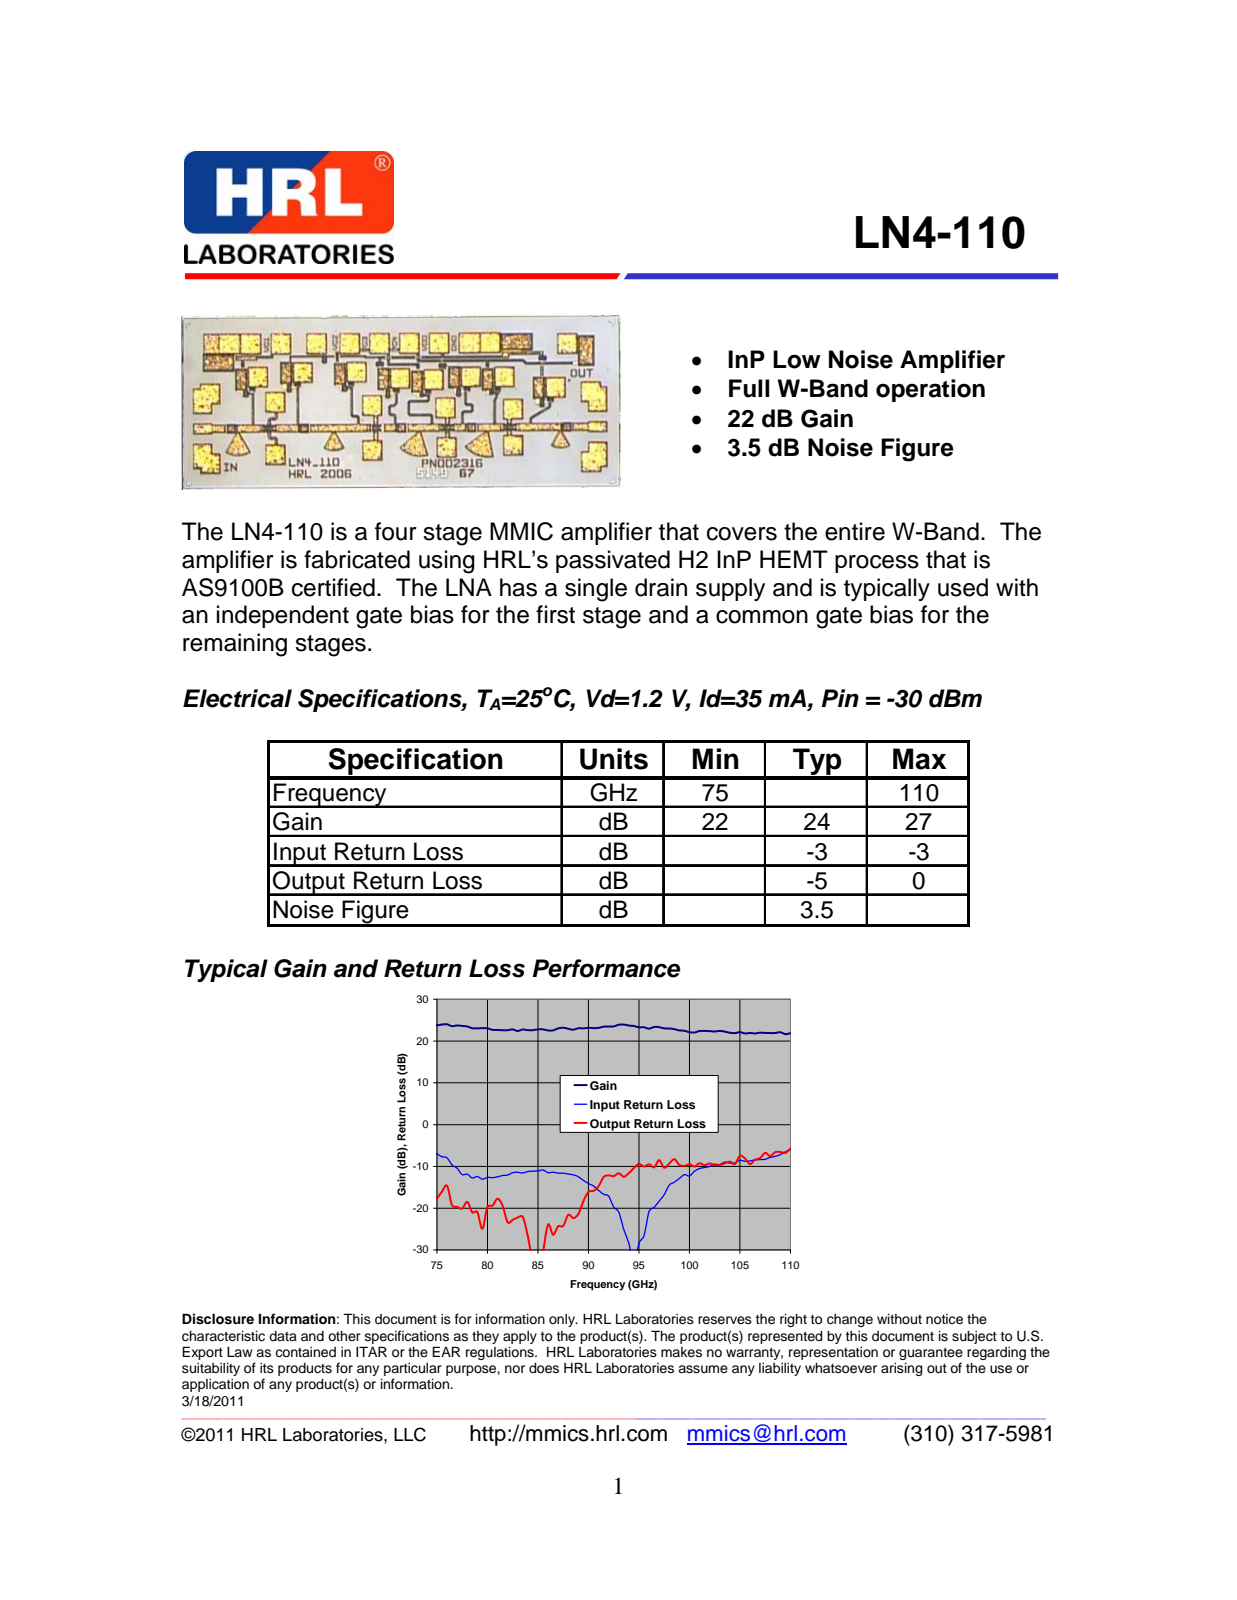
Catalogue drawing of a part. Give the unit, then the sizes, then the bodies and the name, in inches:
Units: inches
Overall size (bounding box): 0.082 × 0.033 × 0.002
Main face-to-face distances: 0.033, 0.082, 0.026, 0.03, 0.016, 0.022, 0.025, 0.017, 0.024, 0.024
Bodies: 1 solid, 767 faces (767 planar, 0 cylindrical, 0 other)
Part name (STEP PRODUCT): LN4-110
STEP written by: Autodesk Inventor 2009 (AUTOMOTIVE_DESIGN)
